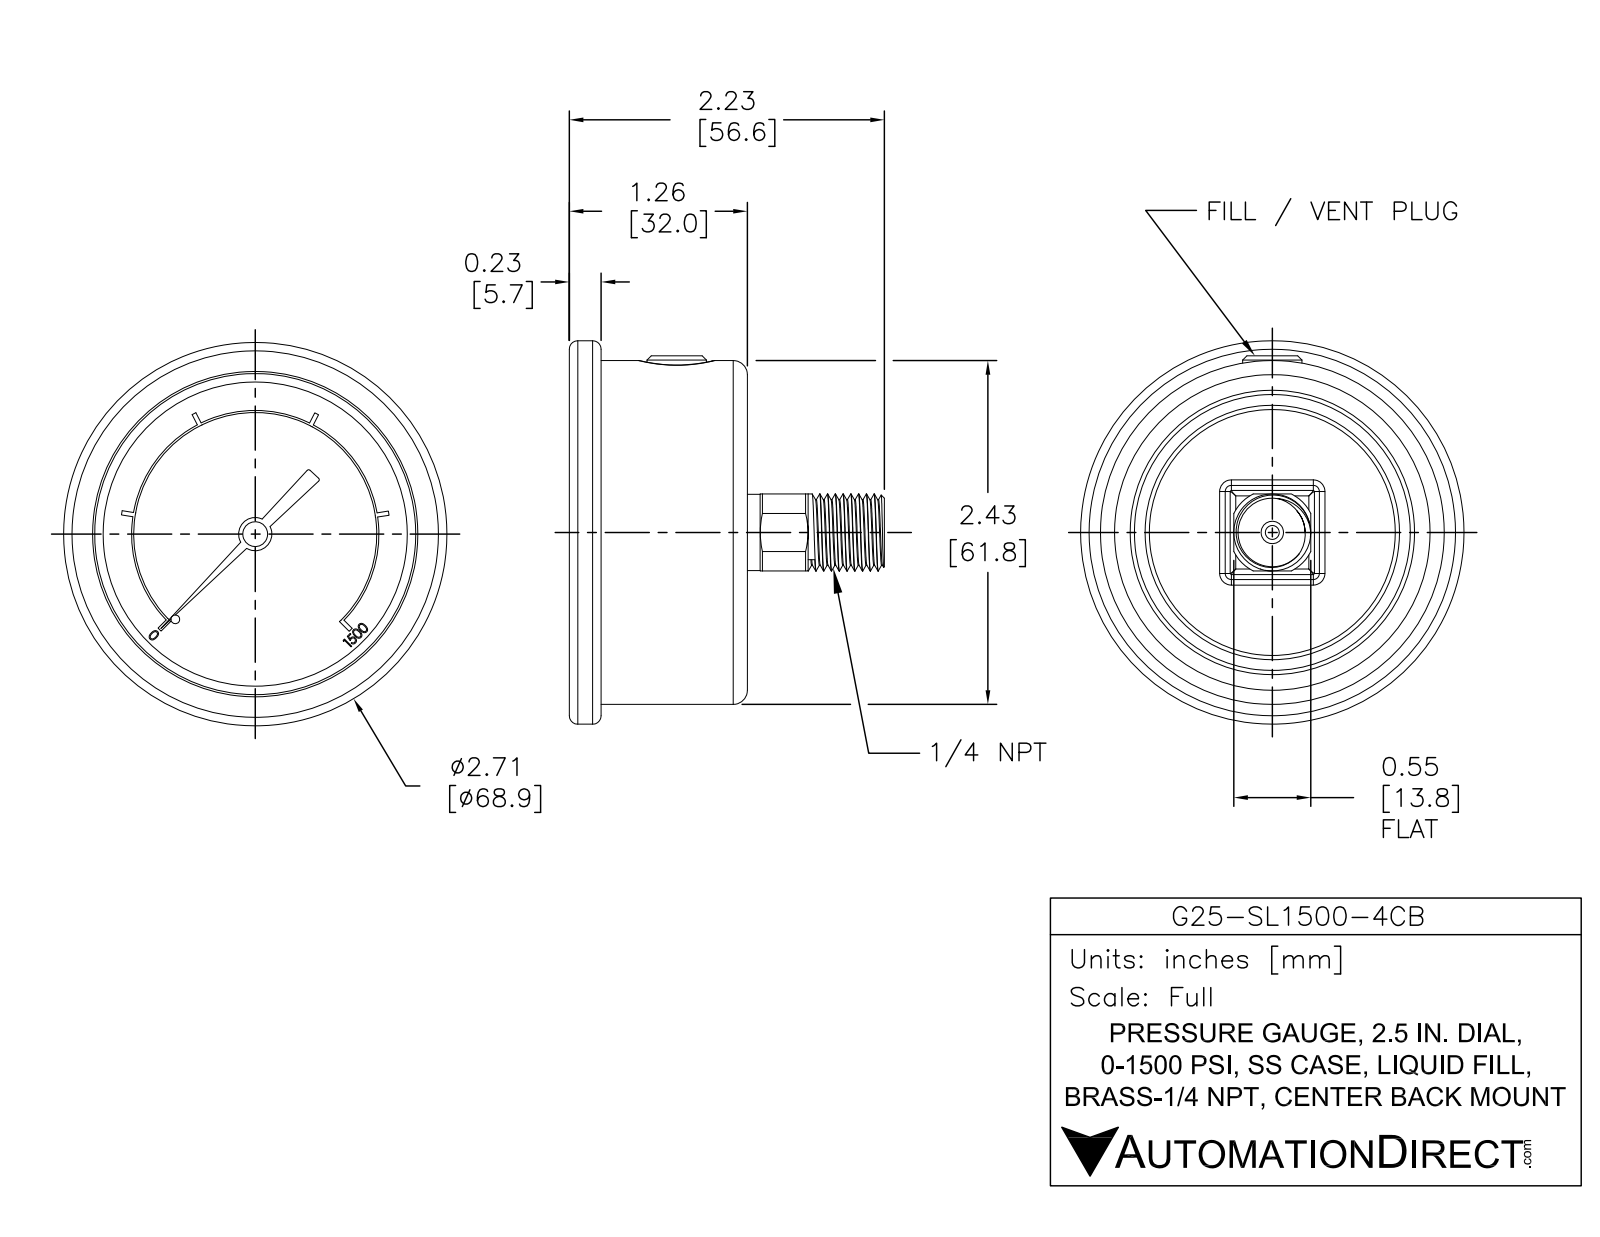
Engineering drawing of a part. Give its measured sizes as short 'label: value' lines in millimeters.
name: G25-SL1500-4CB
written by: SolidWorks 2021 (AUTOMOTIVE_DESIGN)
unit: mm
bodies: 1 solid, 363 faces (215 planar, 83 cylindrical, 65 other)
size: 68.9 × 68.9 × 56.6
volume: 84 690 mm³; area: 16 020 mm²
holes: 1× ⌀1.8, 1× ⌀2.5, 1× ⌀57.7
bosses: 1× ⌀68.9, 1× ⌀61.8, 1× ⌀13.8, 1× ⌀13.7, 1× ⌀10.7, 1× ⌀6, 1× ⌀4.5, 1× ⌀3.6
rounds: 8× R1.5, 2× R0.4, 1× R7.7, 1× R21.8, 1× R22.2
face distances: 24.1, 30.5, 6.4, 1.5, 25.7, 32, 26.3, 24.8, 0.6, 5.7
